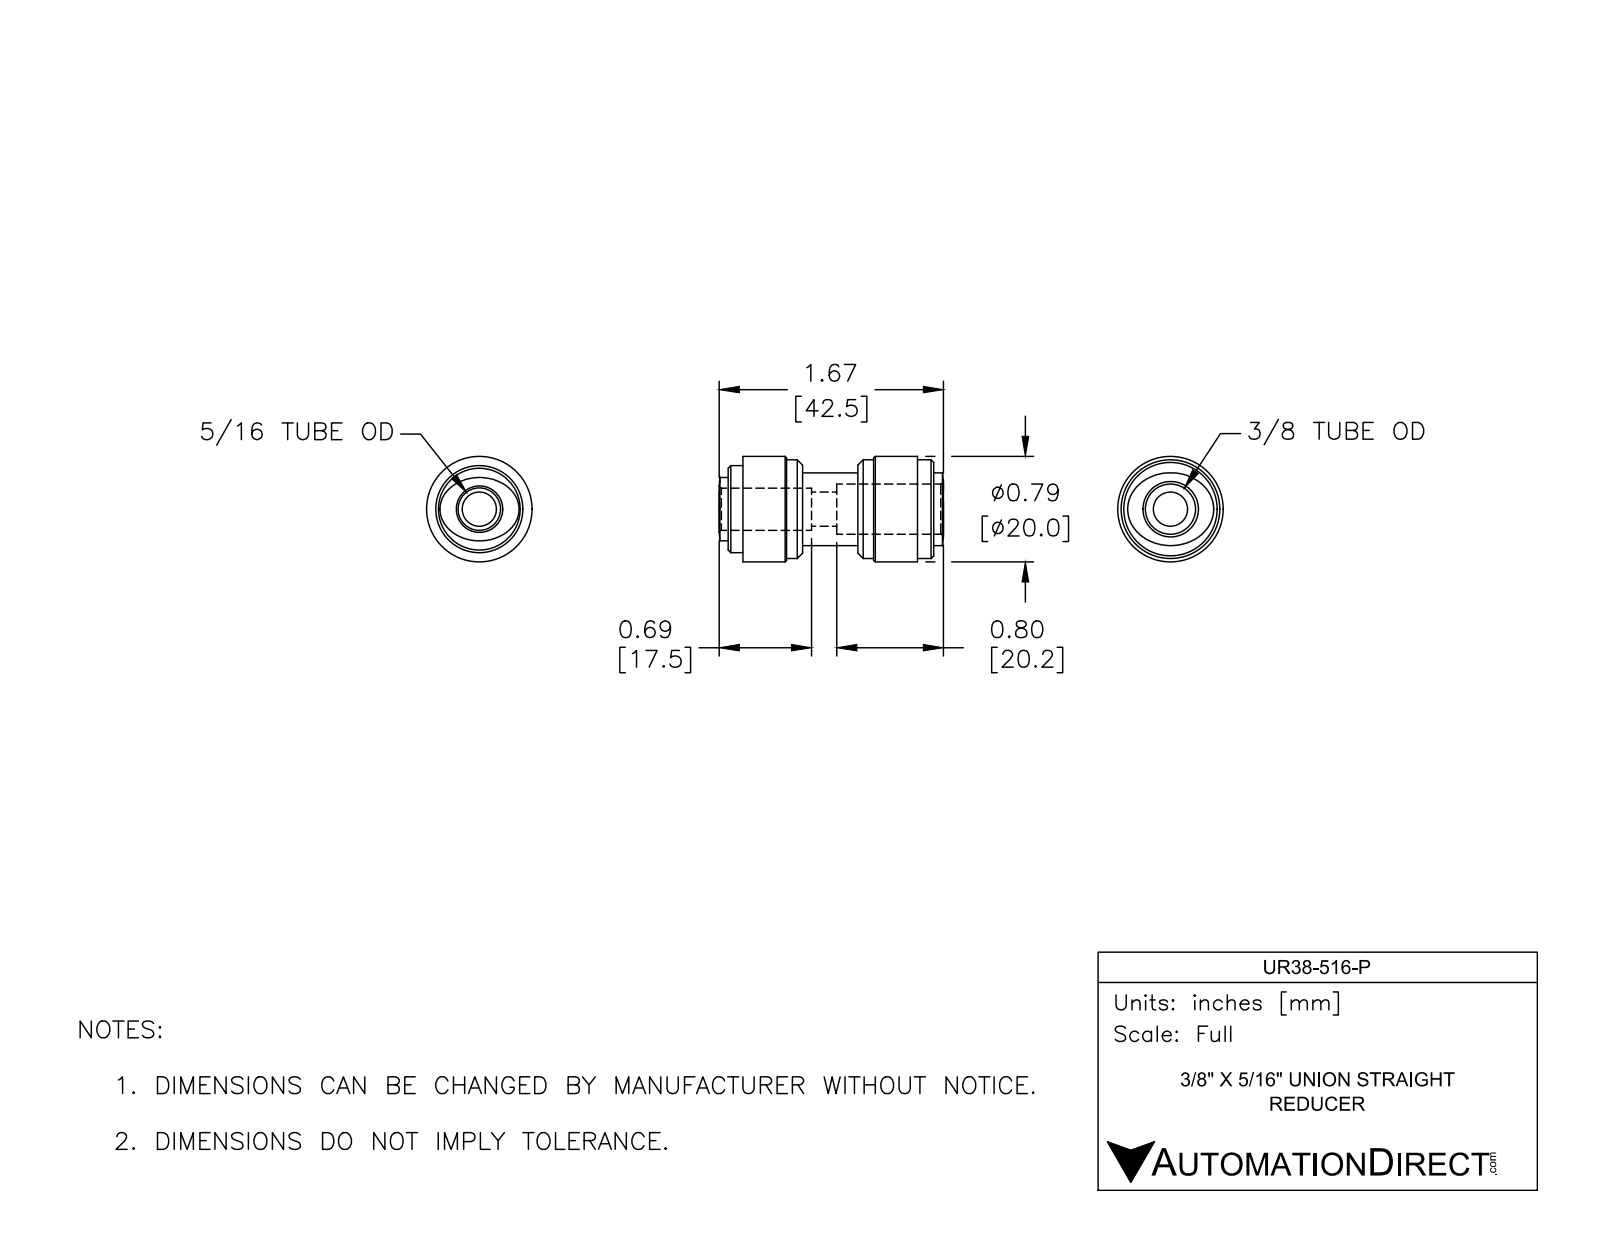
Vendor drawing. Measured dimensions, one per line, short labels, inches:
name: UR38-516-P
written by: SolidWorks 2017 (AUTOMOTIVE_DESIGN)
unit: in
bodies: 1 solid, 54 faces (10 planar, 20 cylindrical, 24 other)
size: 1.673 × 0.787 × 0.787
volume: 0.48 in³; area: 6.534 in²
holes: 1× ⌀0.256, 1× ⌀0.315, 1× ⌀0.374
bosses: 1× ⌀0.787, 1× ⌀0.736, 1× ⌀0.65, 1× ⌀0.543
face distances: 0.445, 0.858, 0.413, 0.567, 0.98, 1.425, 1.535, 0.969, 0.555, 0.11
